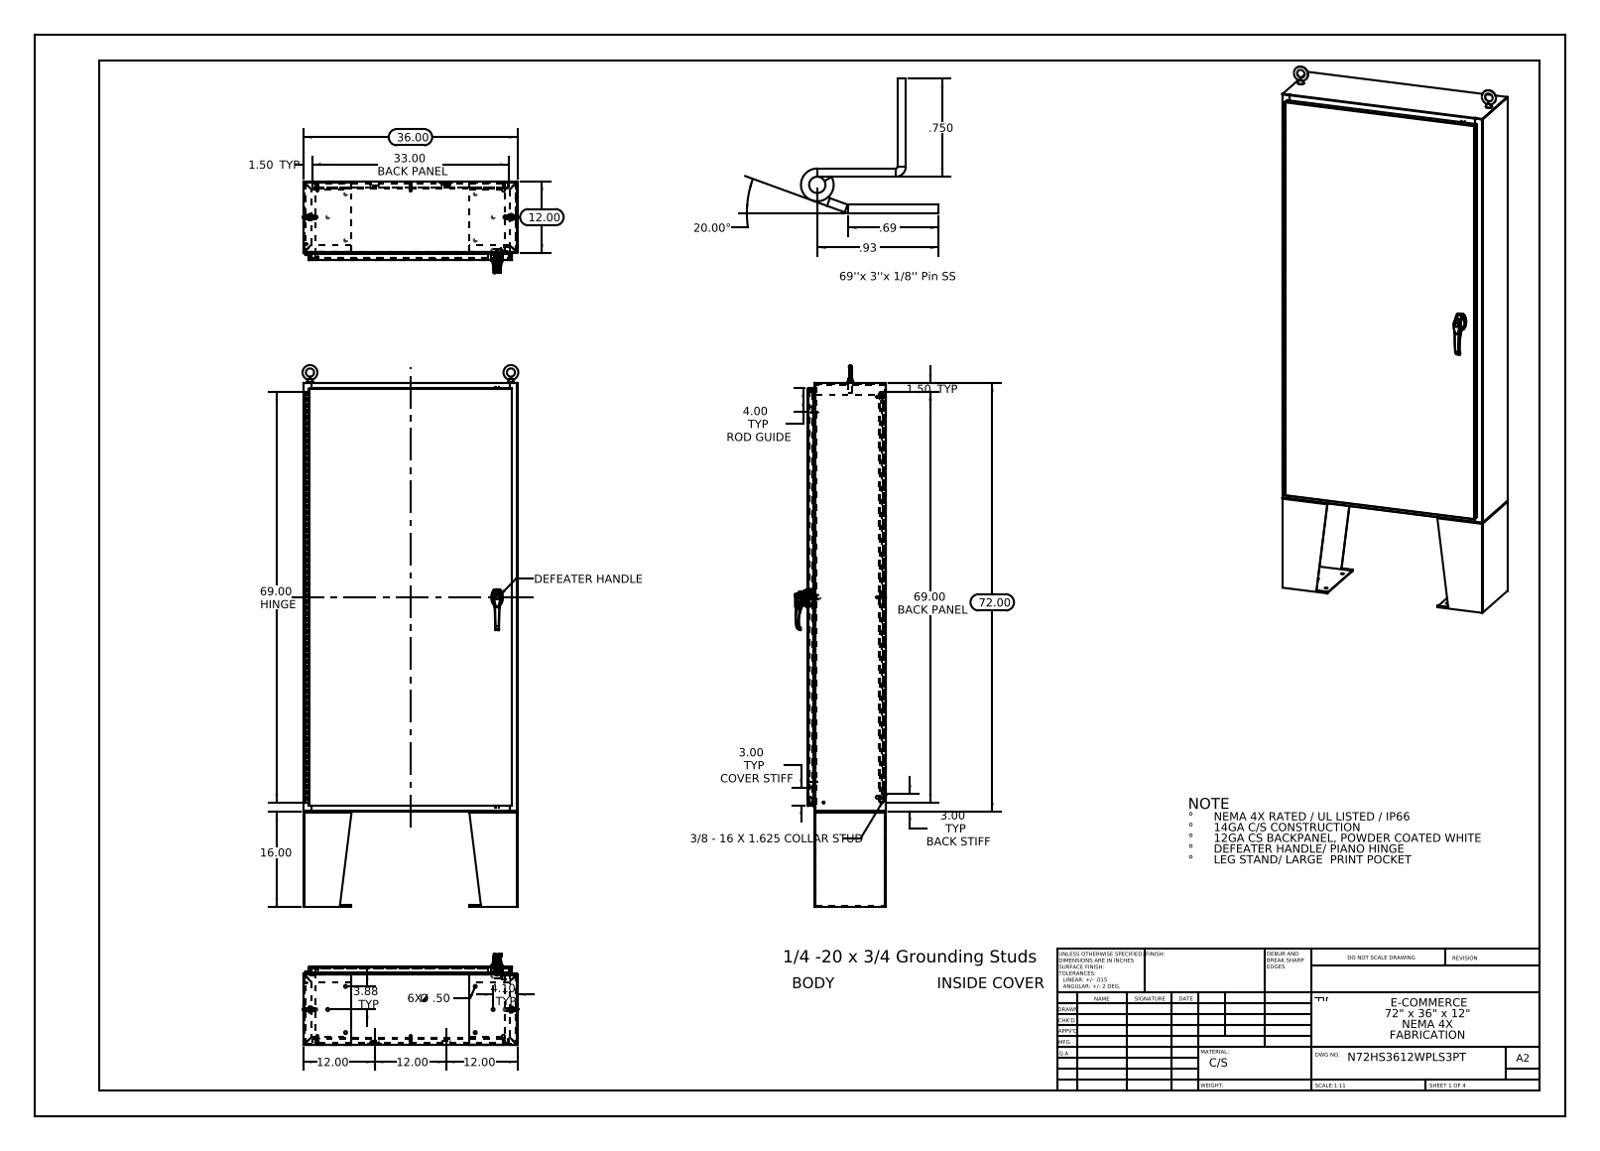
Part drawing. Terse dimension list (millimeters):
name: N72HS3612SSWPLS3PT SD-LSK-Stand; HW-EYE-NH-20425_3014T52; 022151; 00005310_26163101 (+8 more)
written by: SolidWorks 2013 (CONFIG_CONTROL_DESIGN)
unit: mm
bodies: 55 solids, 4096 faces (1673 planar, 1605 cylindrical, 818 other)
size: 2311.4 × 921.3 × 388.8
volume: 17 470 000 mm³; area: 16 580 000 mm²
holes: 14× ⌀12.7, 10× ⌀6.4, 4× ⌀19.1, 3× ⌀3.5, 3× ⌀4.1, 2× ⌀2, 2× ⌀5.2, 2× ⌀8, 2× ⌀11.1, 1× ⌀3.2, 1× ⌀3.2, 1× ⌀5
bosses: 10× ⌀15.9, 10× ⌀4, 10× ⌀3.6, 8× ⌀9.5, 8× ⌀8.4, 3× ⌀8, 3× ⌀6, 1× ⌀30
rounds: 37× R3, 34× R0.3, 33× R0.2, 28× R2.2, 15× R1, 12× R0.7, 8× R1, 8× R3.6
face distances: 1.9, 333.4, 2.6, 331.5, 27.3, 335.3, 25.4, 306.1, 308, 29.9
hole spacings: 181.3, 344.9, 637.4, 745.6, 804.2, 854.1, 941.8, 1166
